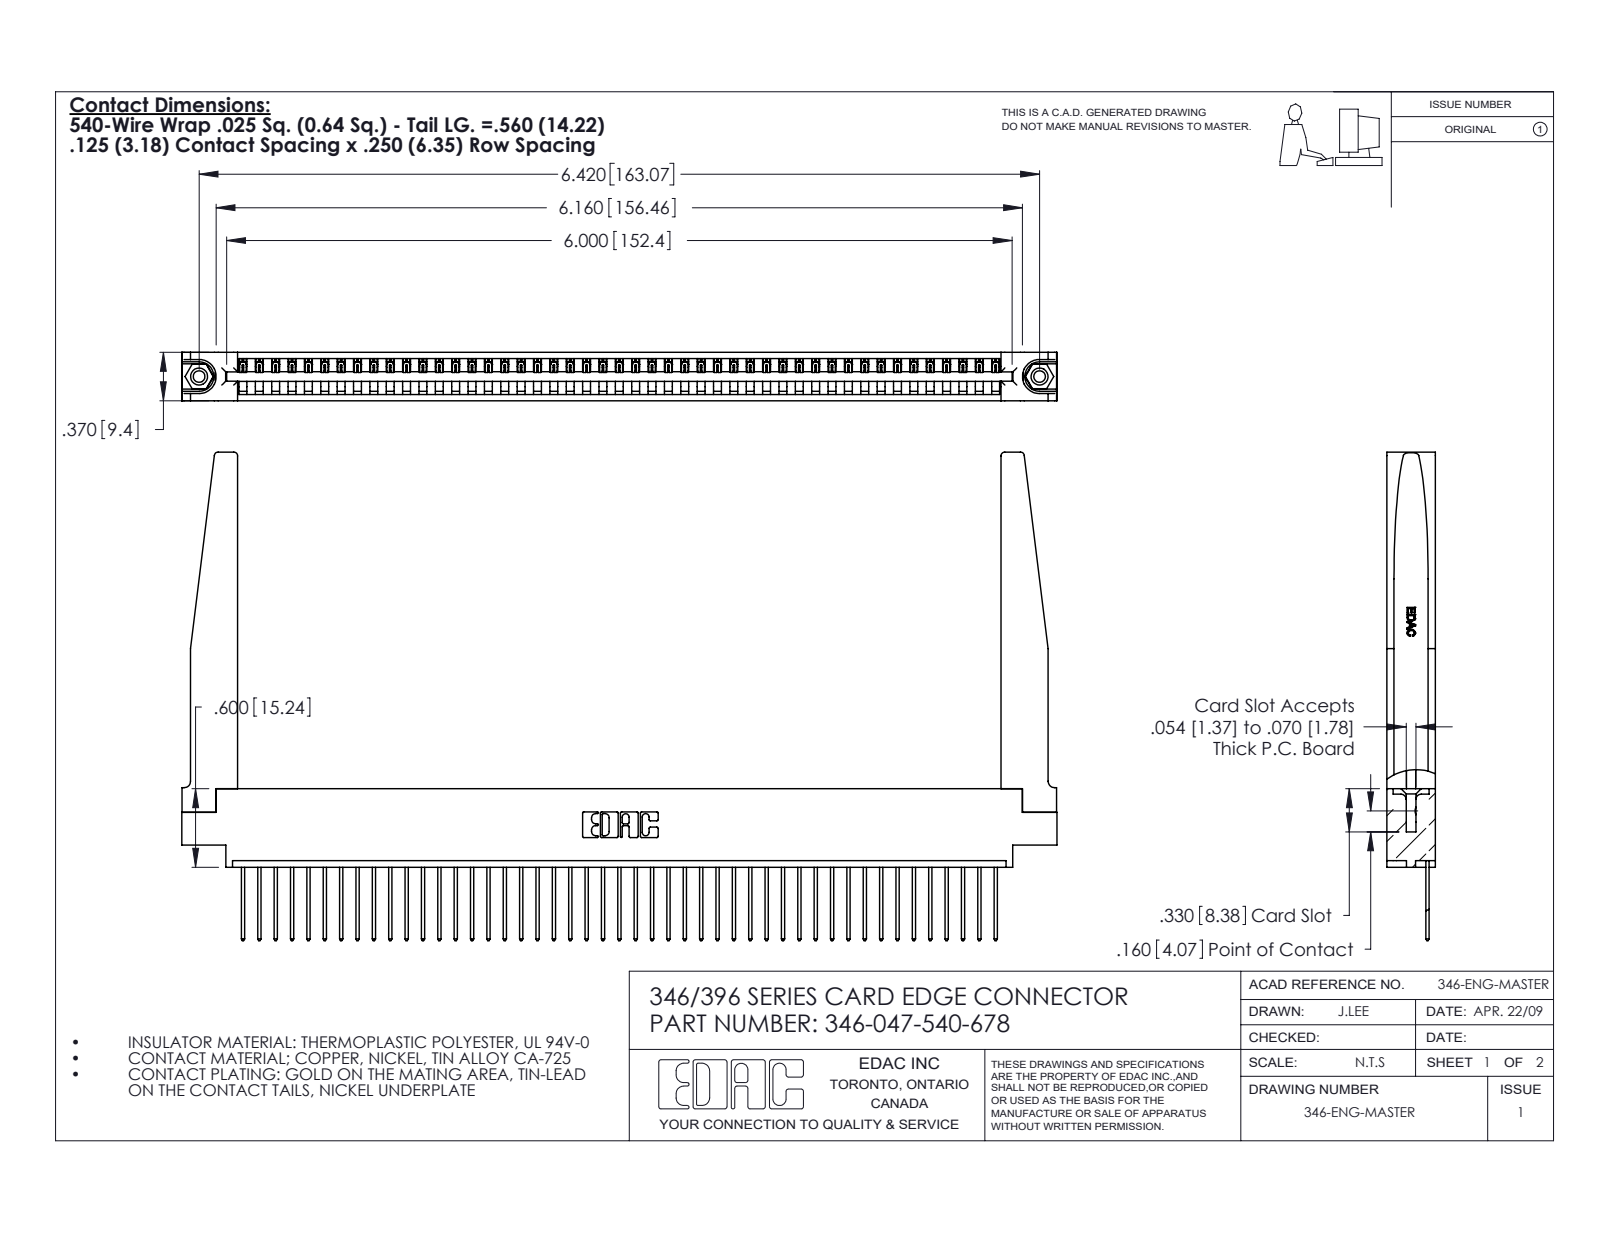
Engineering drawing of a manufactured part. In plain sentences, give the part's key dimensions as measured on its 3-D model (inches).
The part is named "346 Part_0.170 Offset - 0.156 Dia-TH; 345-292-001_345-293-140; 345-250-001_345-250-001-102; 346-220-078_345-220-078 (+1 more)". Its 3-D file was written by "SolidWorks 2020 (CONFIG_CONTROL_DESIGN)". It is 50 solids with 3096 faces: 2112 planar, 932 cylindrical and 52 other. Overall it measures 6.685 by 3.73 by 0.37 inches. Its volume is 0.991 cubic inches and its surface area 42.44 square inches. Round holes: 2 of diameter 0.089, 2 of diameter 0.125, 2 of diameter 0.156, 1 of diameter 0.064. Round bosses or shafts: 2 of diameter 0.155. Partial cylindrical surfaces (rounded edges, fillets, slot ends): 94 of radius 0.006, 94 of radius 0.01, 22 of radius 0.01, 8 of radius 0.03, 6 of radius 0.007, 6 of radius 0.031, 3 of radius 0.026, 2 of radius 0.031. The main face-to-face distances are 0.37, 0.048, 0.322, 0.072, 0.25, 0.148, 0.15, 0.298, 0.025, 0.222. The hole center spacings are 0.246, 6.211, 6.42.
